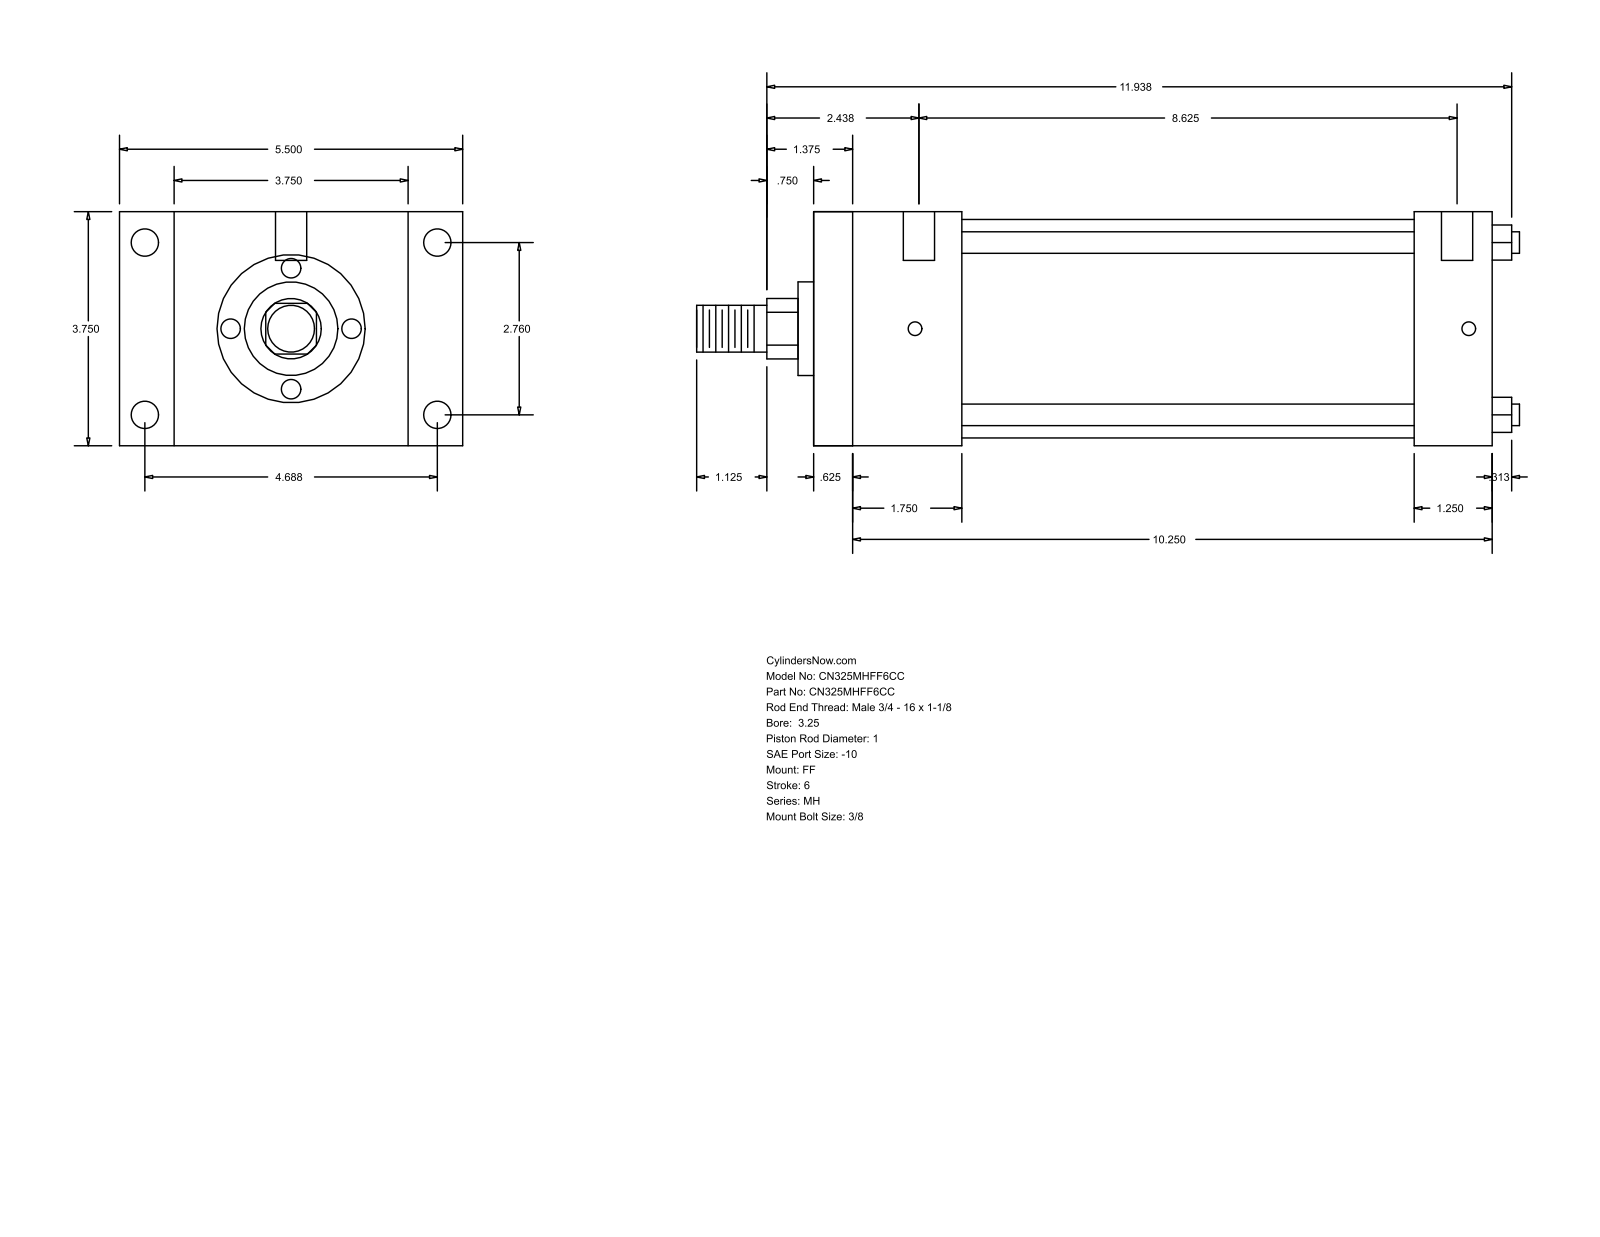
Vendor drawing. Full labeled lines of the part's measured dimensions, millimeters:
Part name (STEP PRODUCT): MH_FF__0325_1
STEP written by: GSSL Pune (CONFIG_CONTROL_DESIGN)
Units: millimetres
Bodies: 0 solids, 92 faces (64 planar, 28 cylindrical, 0 other)
Overall size (bounding box): 334.96 × 139.7 × 95.25
Round holes (diameter × count): ⌀5.56 ×4, ⌀11.13 ×4, ⌀12.7 ×2
Round bosses / shafts (diameter × count): ⌀8.76 ×4, ⌀88.9 ×1, ⌀38.1 ×1, ⌀25.4 ×1, ⌀19.05 ×1
Partial cylindrical surfaces — rounded edges, fillets, slot ends (radius × count): R12.29 ×1
Main face-to-face distances: 95.24, 276.22, 15.87, 260.35, 22.23, 117.47, 244.47, 228.6, 31.75, 60.33
Hole centre spacings: 70.1, 119.06, 138.16, 225.42, 1.58, 4.76, 219.08, 220.66
